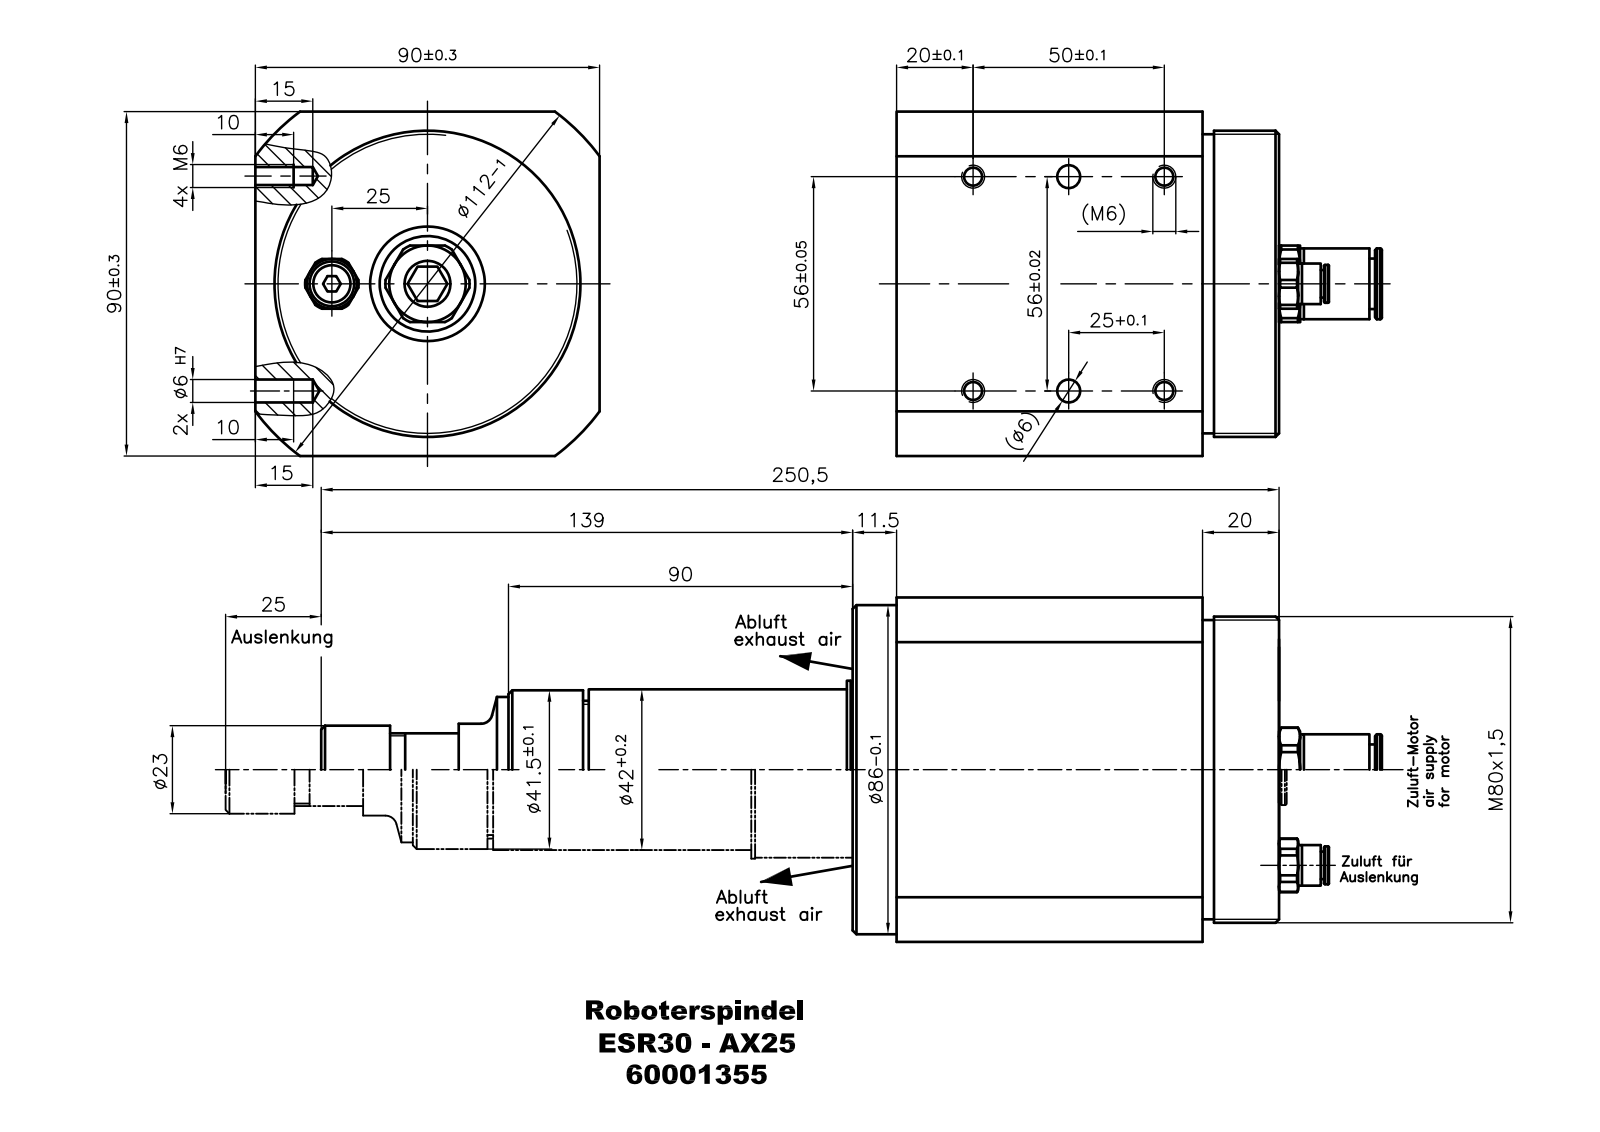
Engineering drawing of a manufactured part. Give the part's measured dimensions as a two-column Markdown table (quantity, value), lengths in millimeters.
| quantity | value |
| --- | --- |
| part name | ESR 30 AX25_60001355 |
| STEP written by | Autodesk Inventor 2008 (AUTOMOTIVE_DESIGN) |
| units | millimeters |
| bodies | 1 solid, 326 faces (150 planar, 78 cylindrical, 98 other) |
| overall size | 276.77 × 90 × 90 |
| volume | 938 089 mm³ |
| surface area | 77 783 mm² |
| round holes (diameter × count) | 6 × 2, 5 × 1, 12 × 1, 19.5 × 1, 30 × 1, 65 × 1 |
| round bosses / shafts (diameter × count) | 86 × 1, 80 × 1, 78.18 × 1, 46.5 × 1, 46 × 1, 42 × 1, 41.5 × 1, 38 × 1 |
| partial cylindrical surfaces (radius × count) | 18.09 × 6, 33.72 × 6, 6.67 × 1, 7 × 1, 11 × 1, 30.12 × 1, 41.68 × 1, 56 × 1 |
| main face-to-face distances | 90, 111.5, 20, 91.5, 11.5, 80, 100, 0.5, 101.5, 181.5 |
| hole center spacings | 25 |
